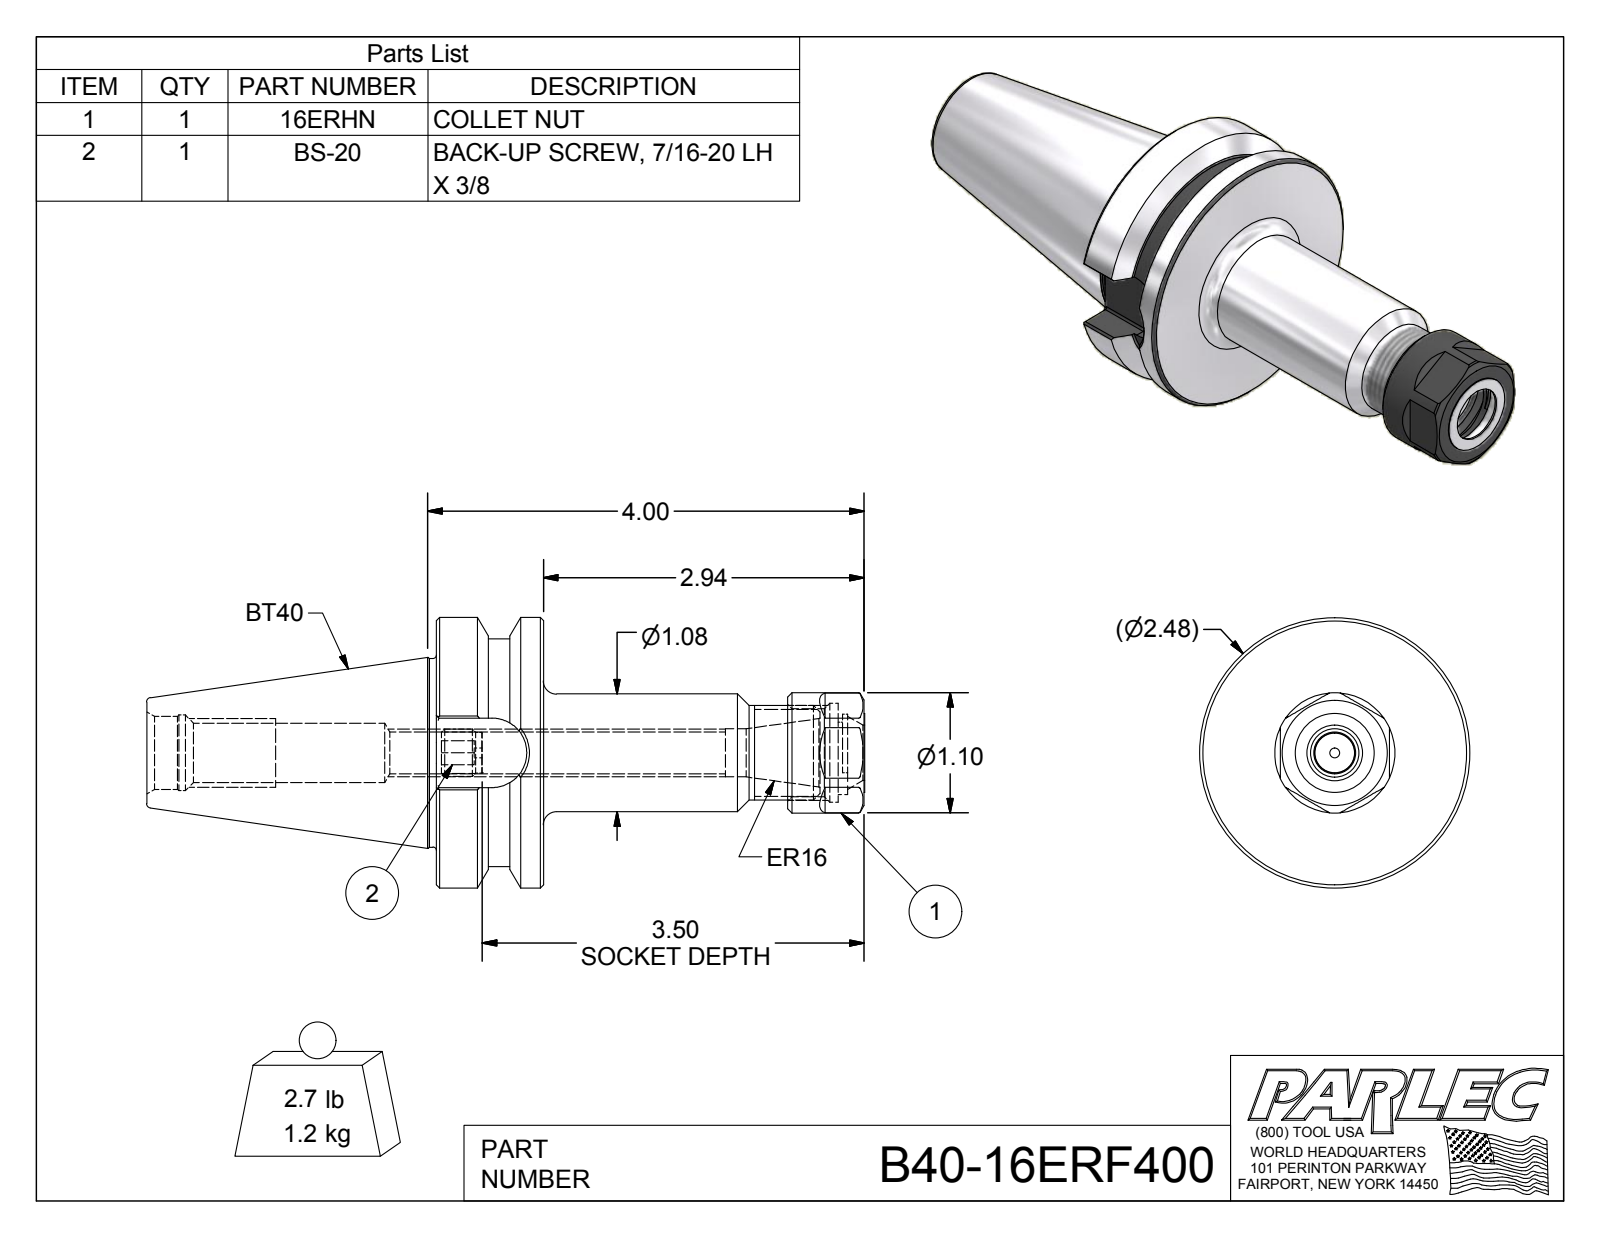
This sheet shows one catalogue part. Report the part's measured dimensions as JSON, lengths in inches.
{"part_name": "B40-16ER4-1; 16ERHN; BS-20; B40-16ERF400", "step_written_by": "Autodesk Inventor 2016 (AUTOMOTIVE_DESIGN)", "units": "inches", "bodies": {"solids": 3, "faces": 121, "planar": 50, "cylindrical": 33, "other": 38}, "overall_size": [6.575, 2.48, 2.48], "volume_in3": 9.504, "surface_area_in2": 51.4, "round_holes": [[0.09, 1], [0.383, 1], [0.44, 1], [0.488, 1], [0.545, 1], [0.67, 1], [0.67, 1], [0.694, 1], [0.807, 1], [0.906, 1]], "round_bosses_or_shafts": [[2.48, 1], [2.087, 1], [1.73, 1], [1.102, 1], [1.08, 1], [0.866, 1], [0.432, 1], [0.372, 1]], "partial_cylinders_radius": [[0.02, 8], [0.285, 1], [0.319, 1], [0.354, 1]], "face_to_face_distances": [0.984, 3.922, 2.938, 0.99, 1.78, 0.395, 1.385, 3.698, 2.714, 0.224], "hole_center_spacings": [0.06]}
